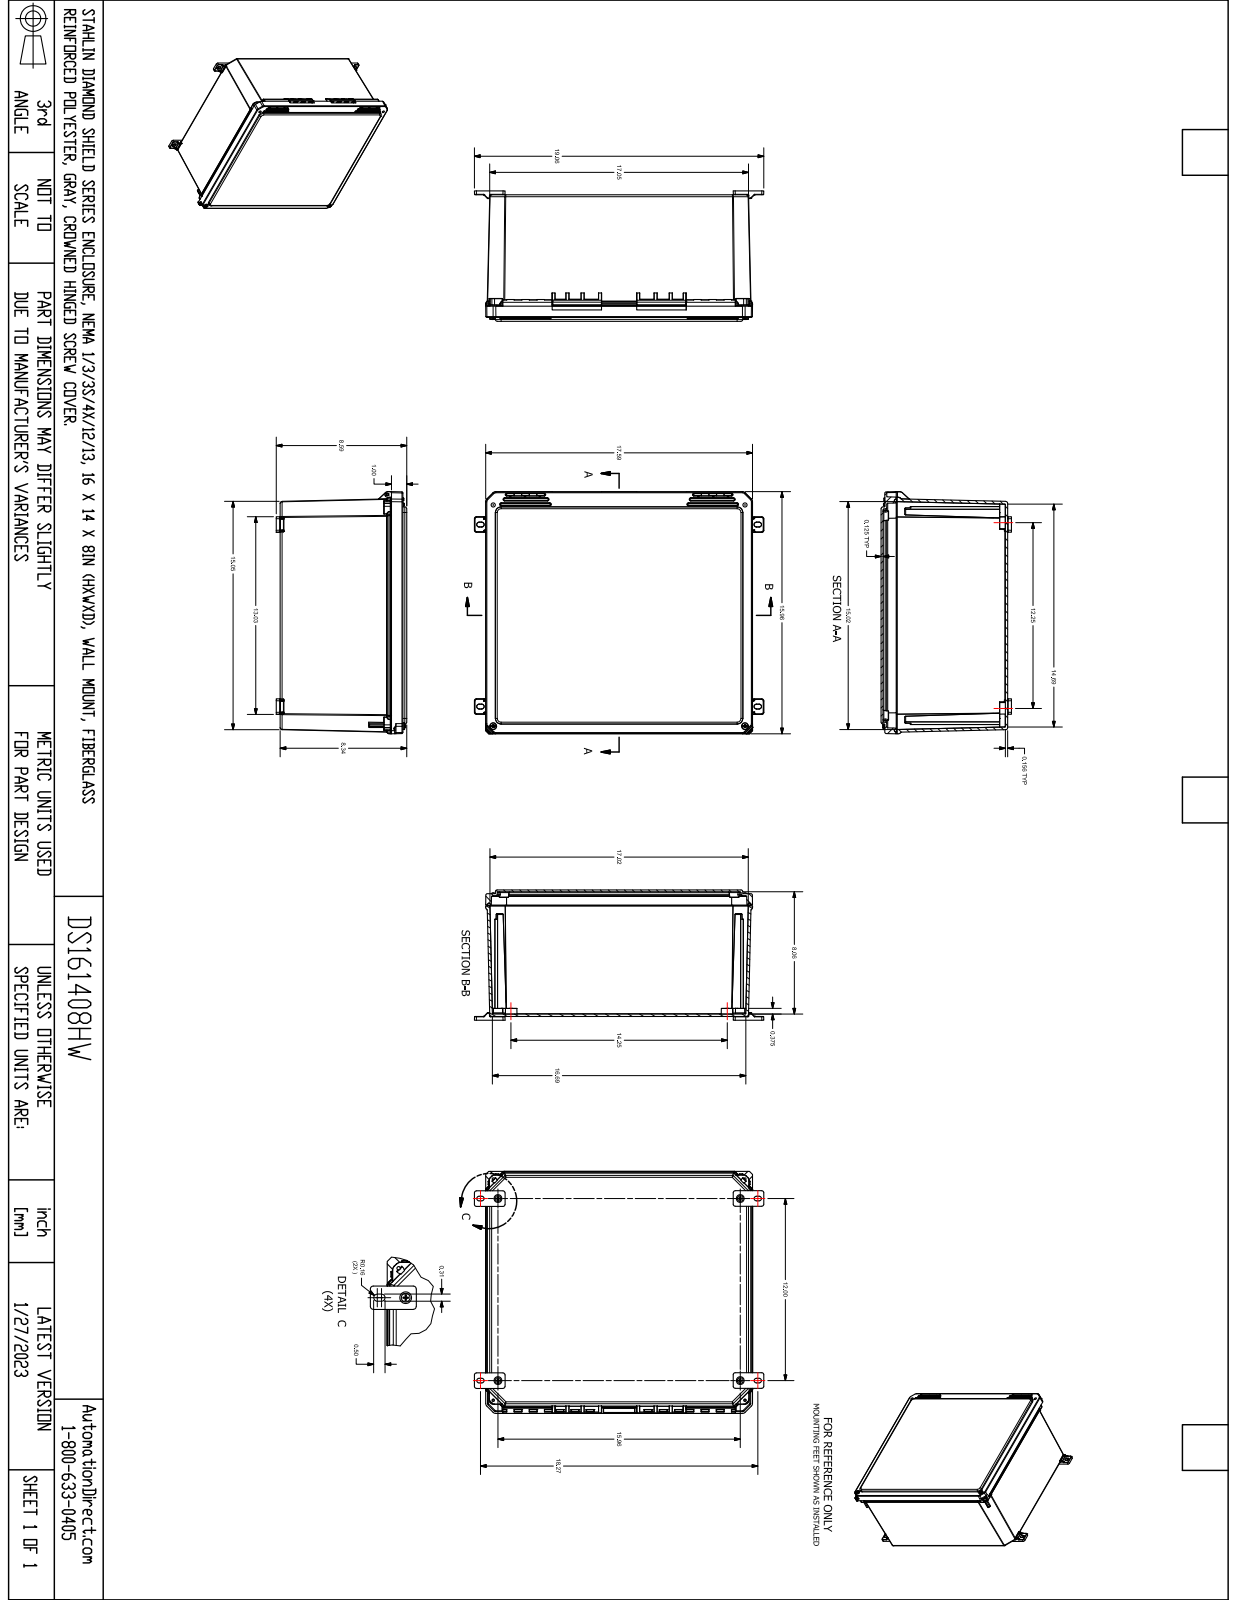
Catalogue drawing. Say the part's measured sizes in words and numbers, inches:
The part is named "FR161408HW". Its 3-D file was written by "SolidWorks 2021 (AUTOMOTIVE_DESIGN)". It is 23 solids with 2243 faces: 693 planar, 889 cylindrical and 661 other. Overall it measures 17.59 by 15.974 by 8.84 inches. Its volume is 184.2 cubic inches and its surface area 2 220 square inches. Round holes: 8 of diameter 0.152, 8 of diameter 0.159, 4 of diameter 0.156, 4 of diameter 0.252, 4 of diameter 0.253, 3 of diameter 0.137, 2 of diameter 0.15, 2 of diameter 0.219, 2 of diameter 0.227, 2 of diameter 0.313. Round bosses or shafts: 8 of diameter 0.27, 4 of diameter 0.262, 2 of diameter 0.45, 2 of diameter 0.209, 2 of diameter 0.199, 1 of diameter 0.435, 1 of diameter 0.435, 1 of diameter 0.135. Partial cylindrical surfaces (rounded edges, fillets, slot ends): 189 of radius 0.01, 94 of radius 0.005, 70 of radius 0.02, 50 of radius 0.03, 24 of radius 0.03, 24 of radius 0.09, 24 of radius 0.096, 22 of radius 0.125. The main face-to-face distances are 0.125, 0.156, 8.183, 8.339, 8.058, 8.214, 0.181, 0.179, 0.18, 0.25. The hole center spacings are 16.584, 15.461, 16.585, 20.439, 12.155, 15.106, 19.37, 0.865.
